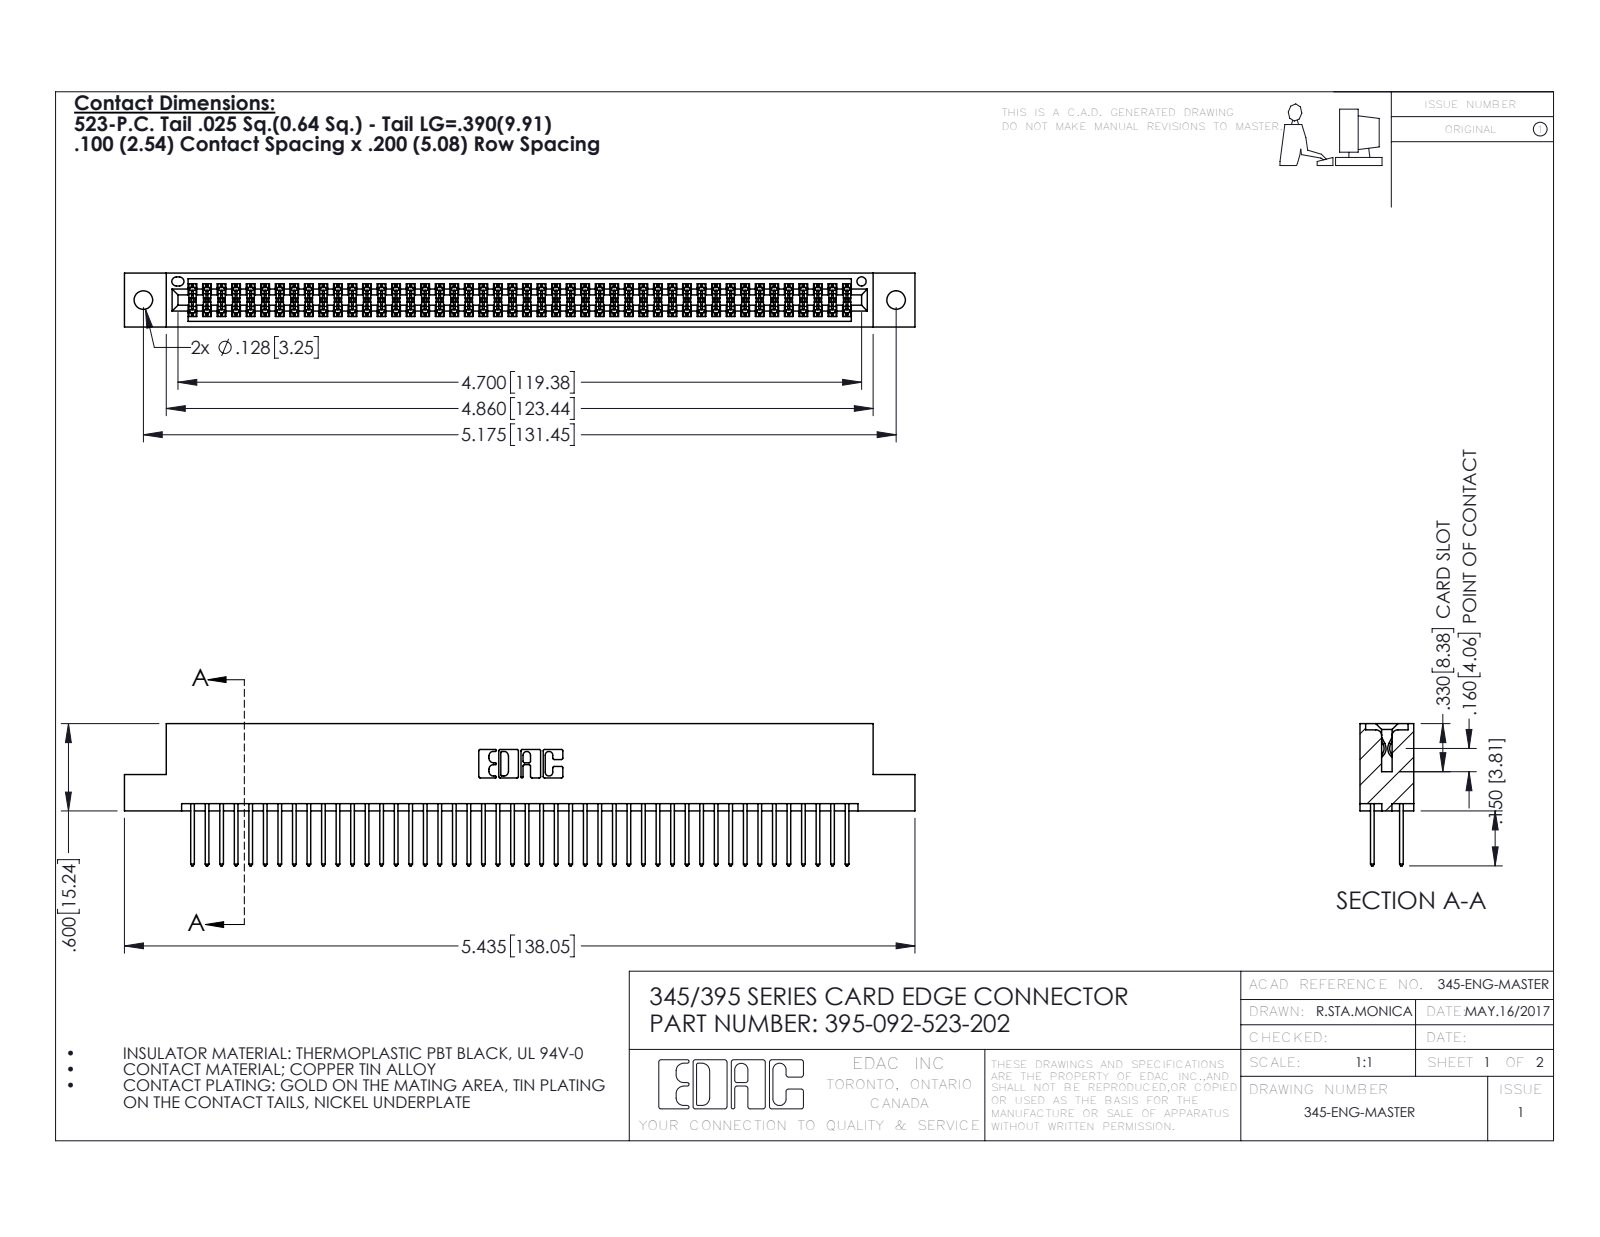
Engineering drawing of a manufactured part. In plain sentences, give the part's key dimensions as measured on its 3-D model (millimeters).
The part is named "345 Part_Flush Mounting Lugs - 0.128 Dia; 345-292-001_345-293-123; 395-092-523-202". Its 3-D file was written by "SolidWorks 2016 (CONFIG_CONTROL_DESIGN)". It is 93 solids with 4726 faces: 3116 planar, 1610 cylindrical and 0 other. Overall it measures 138 by 24.8 by 9.4 millimeters. Its volume is 13 600 cubic millimeters and its surface area 20 750 square millimeters. Round holes: 2 of diameter 3.3, 1 of diameter 1.6. Partial cylindrical surfaces (rounded edges, fillets, slot ends): 138 of radius 0.2, 92 of radius 0.3, 22 of radius 0.3, 6 of radius 0.2, 6 of radius 0.8, 3 of radius 0.7, 2 of radius 0.4, 2 of radius 0.5. The main face-to-face distances are 7.6, 1.8, 5.1, 2.5, 6.9, 0.6, 9.4, 5.7, 4.4, 3.8. The hole center spacings are 6.9, 125.5, 131.4.
